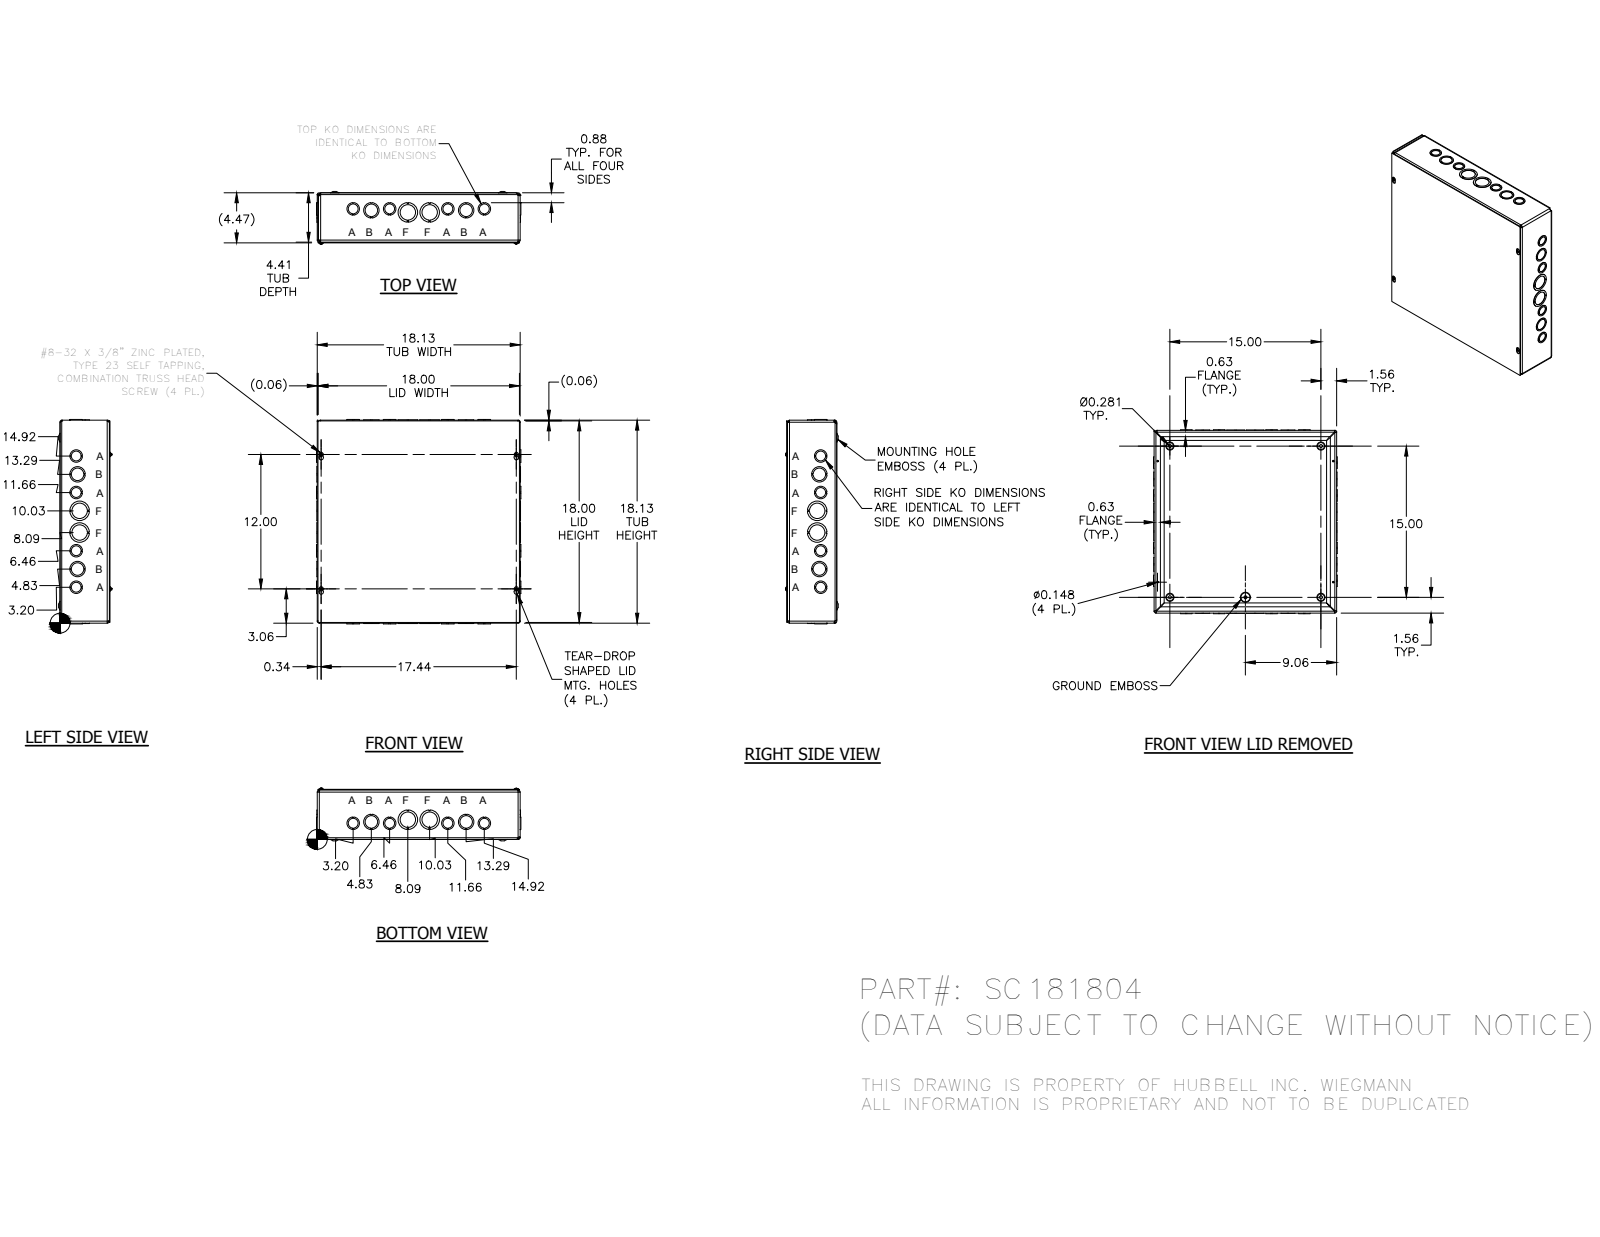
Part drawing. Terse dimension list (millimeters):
name: SC1818BKP; SC181804WRA; SC1818LID; 34056 (+1 more)
written by: Autodesk Inventor 2014 (AUTOMOTIVE_DESIGN)
unit: mm
bodies: 38 solids, 1254 faces (837 planar, 259 cylindrical, 158 other)
size: 463.52 × 463.52 × 119.2
holes: 12× ⌀28.57, 8× ⌀22.22, 8× ⌀34.92, 4× ⌀3.76, 4× ⌀7.62, 4× ⌀44.45, 1× ⌀4.19
bosses: 4× ⌀9.75, 4× ⌀4.17, 1× ⌀5.8
rounds: 12× R3.17, 8× R4.75, 4× R1.4, 4× R1.57, 4× R2.38, 4× R2.97, 4× R3.15, 4× R3.96
face distances: 1.57, 110.32, 111.89, 1.59, 111.91, 113.48, 458.8, 460.37, 457.23, 3.16
hole spacings: 41.52, 42.15, 49.09, 82.94, 91.03, 132.17, 173.51, 214.88
